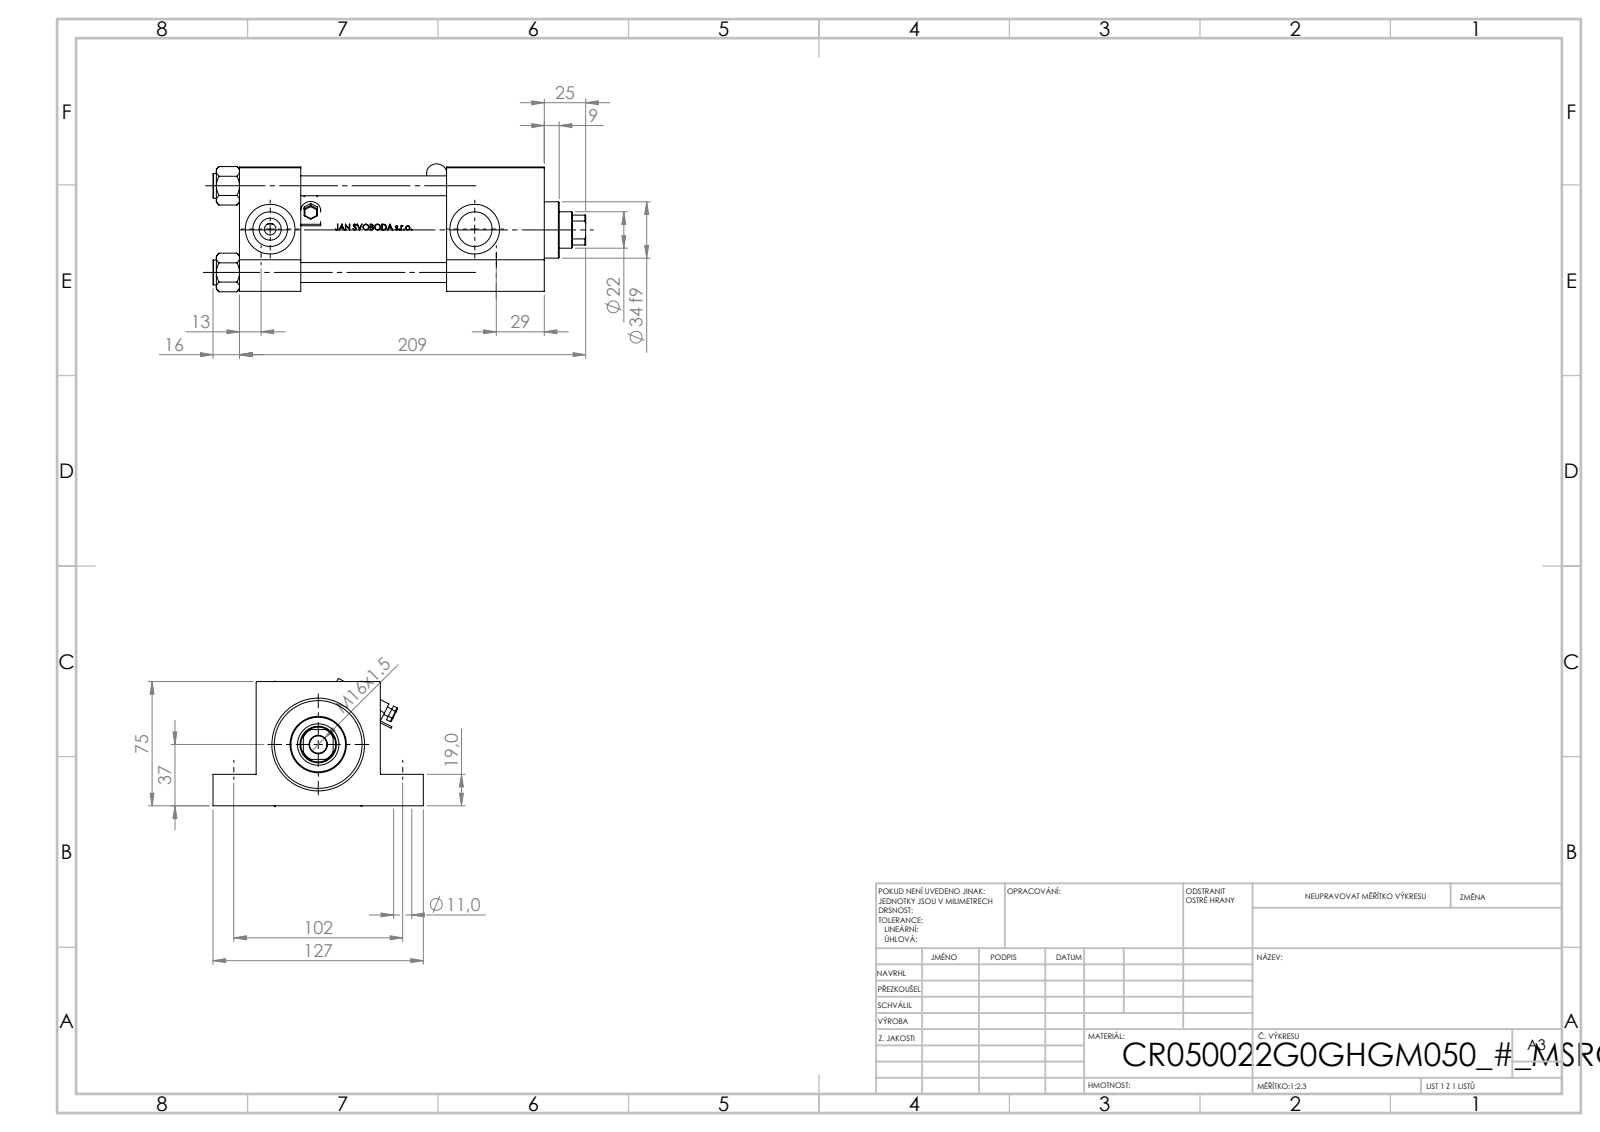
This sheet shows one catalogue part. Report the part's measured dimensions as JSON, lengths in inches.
{"part_name": "V215CR_VCP_G; V215CR_G_TYCINKA; NUT_M5_G; MSRF_MSRG1 (+2 more)", "step_written_by": "SolidWorks 2019 (CONFIG_CONTROL_DESIGN)", "units": "inches", "bodies": {"solids": 13, "faces": 1151, "planar": 467, "cylindrical": 152, "other": 532}, "overall_size": [8.858, 5, 3.037], "volume_in3": 49.01, "surface_area_in2": 279.6, "round_holes": [[0.433, 4], [0.472, 4], [0.276, 2], [0.825, 2], [1.181, 2], [0.413, 1], [0.866, 1], [0.984, 1], [1.614, 1], [1.969, 1], [2.087, 1]], "round_bosses_or_shafts": [[0.591, 4], [0.197, 2], [0.098, 2], [2.205, 1], [1.339, 1]], "partial_cylinders_radius": [[0.02, 12], [0.236, 5], [0.413, 1]], "face_to_face_distances": [2.953, 1.457, 7.244, 5.787, 0.748, 2.205, 3.465, 3.976, 4.921, 2.323], "hole_center_spacings": [2.059, 1.442, 1.47, 2.912, 4.016, 5.591, 6.883, 4.862]}
